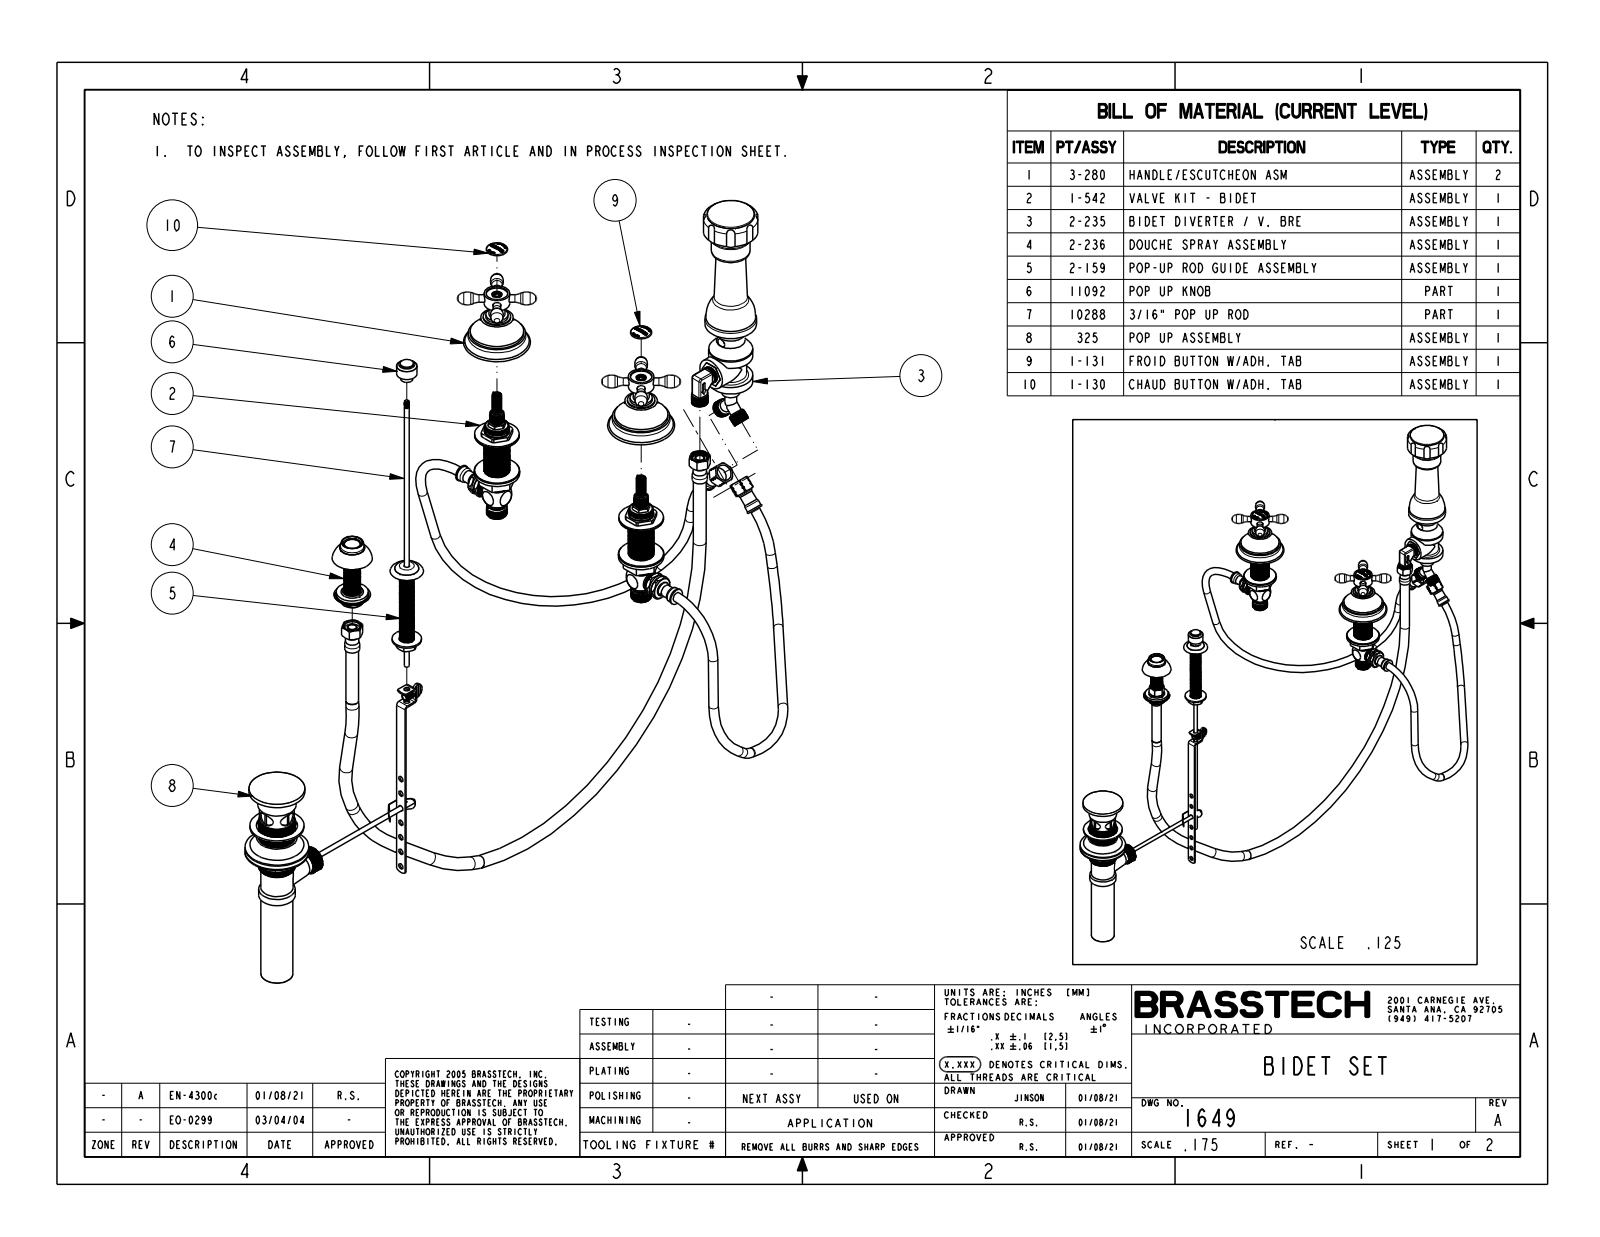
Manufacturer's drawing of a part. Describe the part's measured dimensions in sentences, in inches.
The part is named "1649". Its 3-D file was written by "CREO PARAMETRIC BY PTC INC, 2018400 (CONFIG_CONTROL_DESIGN)". It is 7 solids with 999 faces: 433 planar, 332 cylindrical and 234 other. Overall it measures 22.856 by 10.625 by 5.353 inches. Its volume is 21.99 cubic inches and its surface area 101.5 square inches. Round holes: 2 of diameter 0.85, 1 of diameter 0.625, 1 of diameter 0.792, 1 of diameter 0.94. Round bosses or shafts: 8 of diameter 0.3, 2 of diameter 2.1, 2 of diameter 1.075, 2 of diameter 1, 2 of diameter 0.875, 2 of diameter 0.625, 2 of diameter 0.4, 1 of diameter 2.025. Partial cylindrical surfaces (rounded edges, fillets, slot ends): 28 of radius 0.011, 17 of radius 0.025, 14 of radius 0.006, 14 of radius 0.015, 10 of radius 0.005, 9 of radius 0.014, 8 of radius 0.006, 8 of radius 0.013. The main face-to-face distances are 2.355, 0.475, 1.88, 1.375, 0.9, 0.98, 2.36, 1.885, 0.985, 1.225. The hole center spacings are 12.647, 8.
